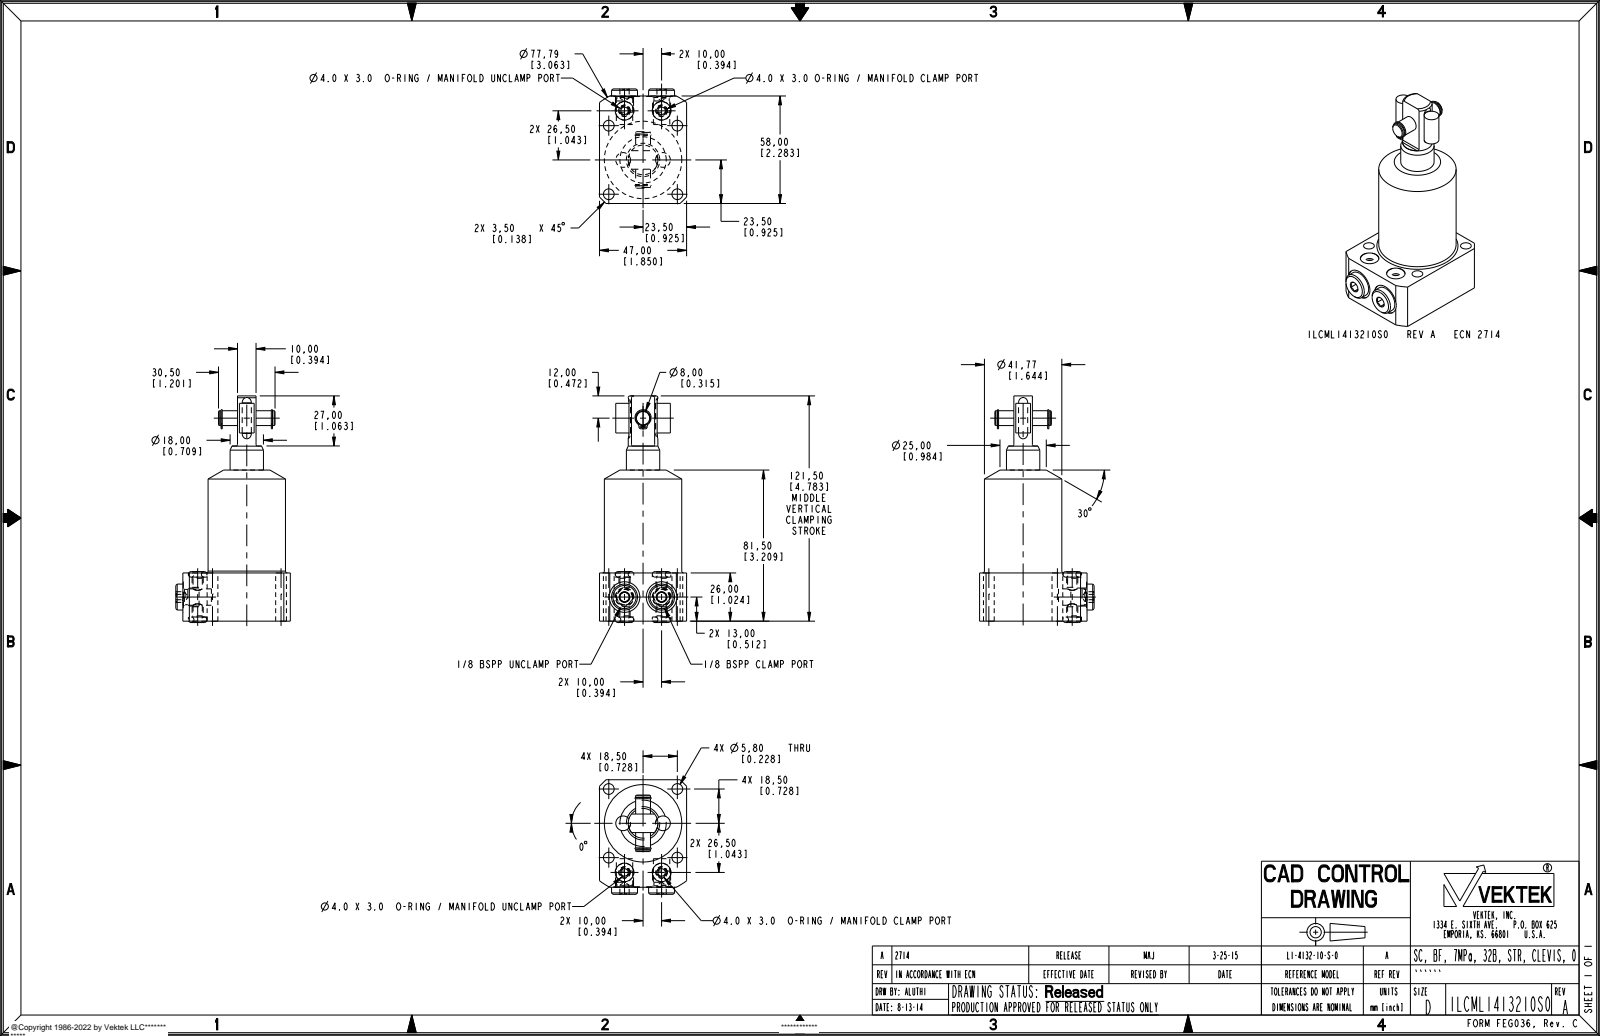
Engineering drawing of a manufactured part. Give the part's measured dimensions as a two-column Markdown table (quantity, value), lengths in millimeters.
| quantity | value |
| --- | --- |
| part name | ILCML1413210S0 |
| STEP written by | PRO/ENGINEER BY PARAMETRIC TECHNOLOGY CORPORATION, 2013320 (AUTOMOTIVE_DESIGN) |
| units | millimeters |
| bodies | 7 solids, 234 faces (80 planar, 98 cylindrical, 56 other) |
| overall size | 122.25 × 61.81 × 47 |
| volume | 149 499 mm³ |
| surface area | 26 707 mm² |
| round holes (diameter × count) | 5.8 × 4, 1.04 × 2, 5 × 2, 8.84 × 2, 10 × 2, 16.5 × 2 |
| round bosses / shafts (diameter × count) | 14 × 2, 9.73 × 2, 8.25 × 2, 7.95 × 2, 6 × 2, 41.77 × 1, 18 × 1, 16 × 1 |
| partial cylindrical surfaces (radius × count) | 0.8 × 2, 1.04 × 2, 2.32 × 2, 3.98 × 2, 4.37 × 1, 38.9 × 1 |
| main face-to-face distances | 47, 26, 58, 10, 28.5, 18.5, 39.5, 29.5, 57.75, 81.5 |
| hole center spacings | 37, 11.67, 20, 29.6, 45.8, 52.33, 53.27, 92.19 |
